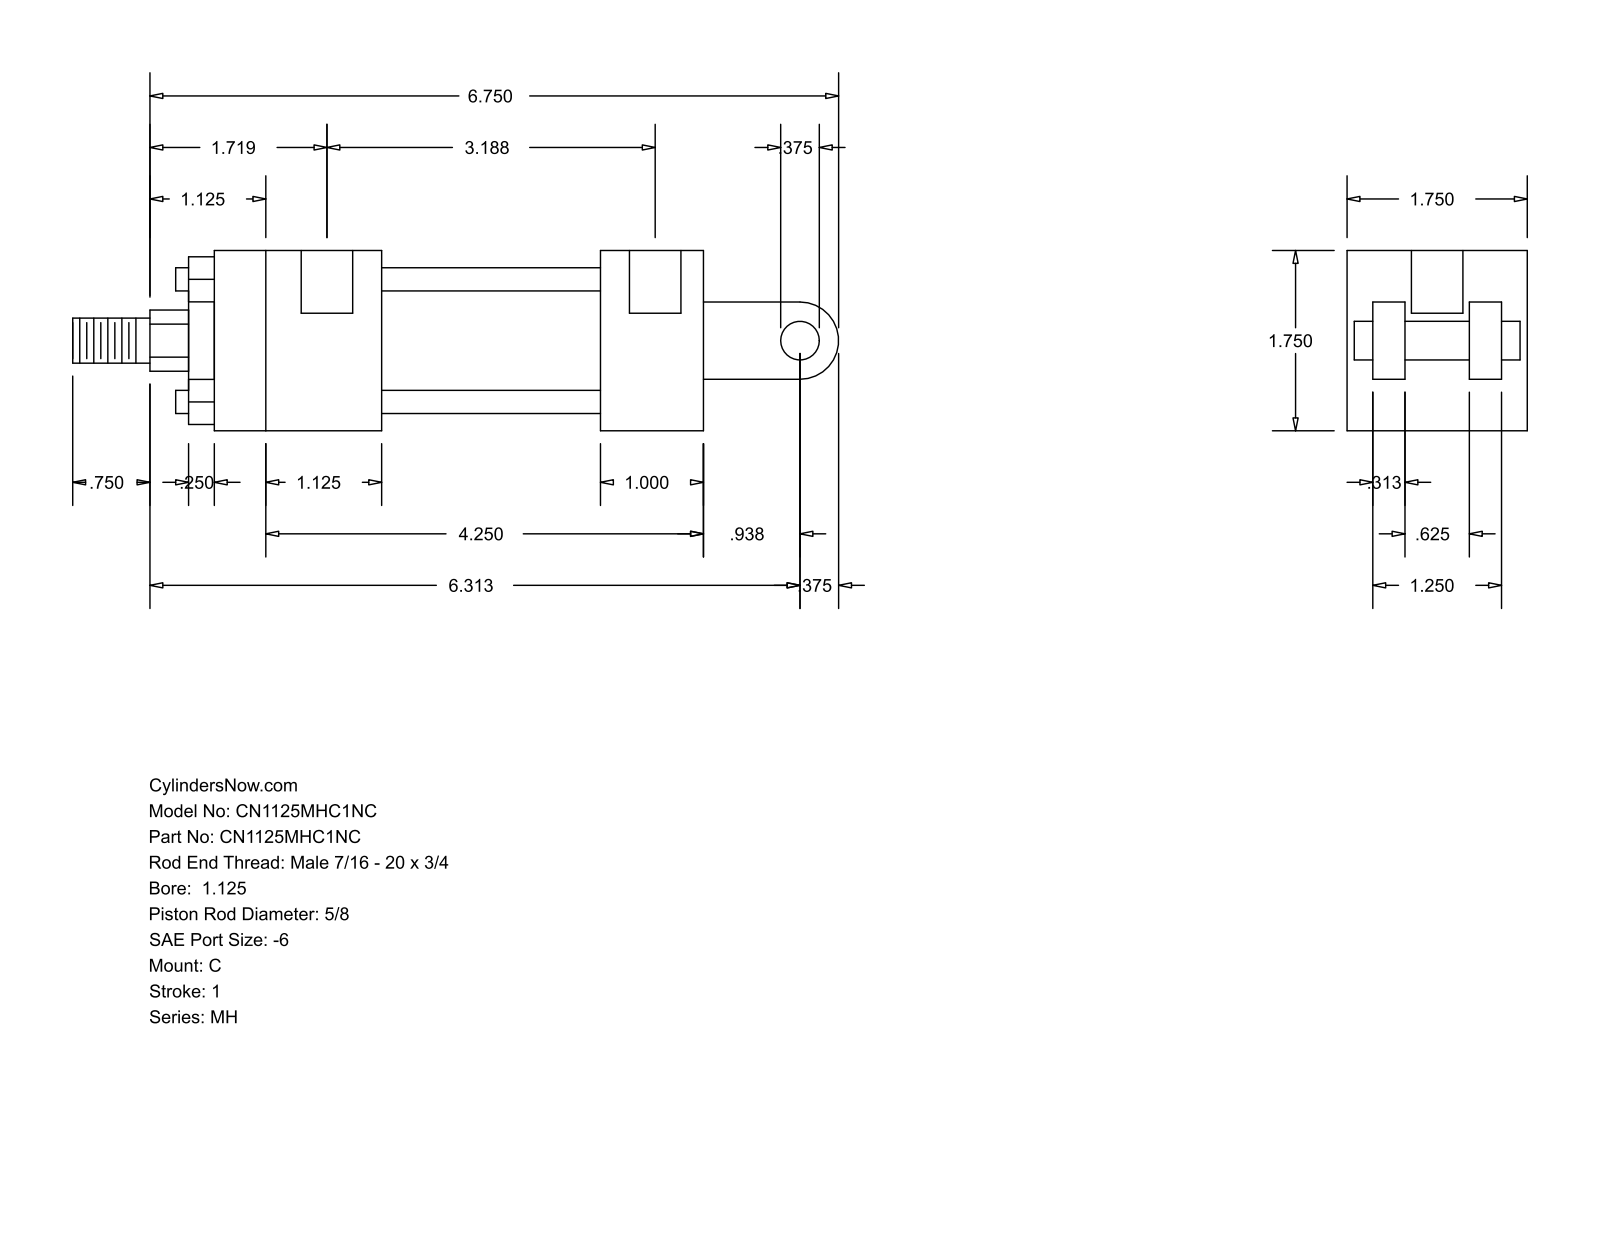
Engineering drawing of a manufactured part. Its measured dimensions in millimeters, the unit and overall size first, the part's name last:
Units: millimetres
Overall size (bounding box): 188.91 × 44.45 × 44.45
Round holes (diameter × count): ⌀5.56 ×4, ⌀12.7 ×2
Round bosses / shafts (diameter × count): ⌀5.71 ×4, ⌀34.92 ×1, ⌀28.57 ×1, ⌀15.88 ×1, ⌀11.11 ×1, ⌀9.53 ×1
Partial cylindrical surfaces — rounded edges, fillets, slot ends (radius × count): R7.54 ×1, R9.53 ×1
Main face-to-face distances: 44.46, 6.35, 31.76, 14.29, 30.17, 38.11, 7.94, 23.82, 41.27, 12.7
Hole centre spacings: 77.79, 3.17, 80.96
Bodies: 0 solids, 99 faces (70 planar, 29 cylindrical, 0 other)
Part name (STEP PRODUCT): MH_C__0112_0.625
STEP written by: GSSL Pune (CONFIG_CONTROL_DESIGN)
